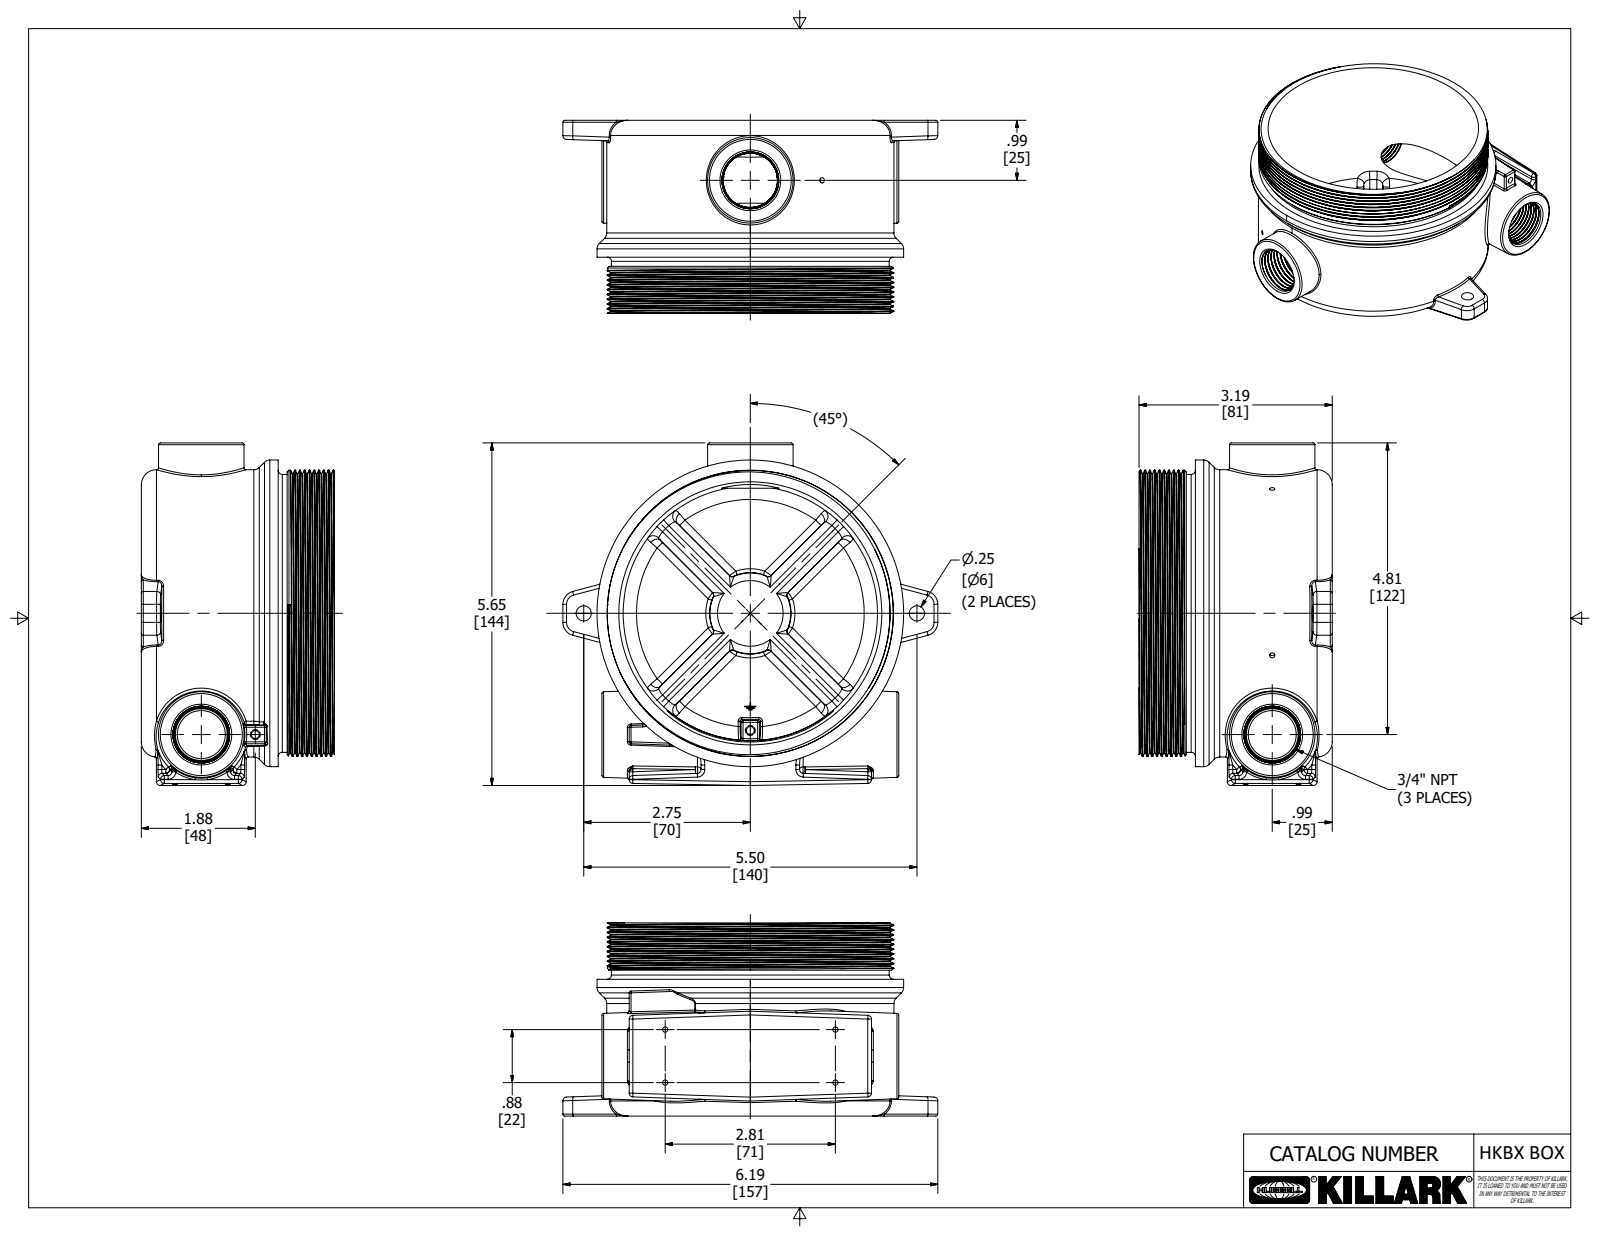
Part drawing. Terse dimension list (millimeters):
name: 51641ABAM for web
written by: Autodesk Inventor 2020 (AUTOMOTIVE_DESIGN)
unit: mm
bodies: 4 solids, 546 faces (207 planar, 96 cylindrical, 243 other)
size: 633.7 × 379.1 × 81
volume: 301 400 mm³; area: 302 100 mm²
holes: 2× ⌀3.3, 2× ⌀6.4, 1× ⌀20.1, 1× ⌀110.2
bosses: 1× ⌀128.5, 1× ⌀120.4, 1× ⌀120, 1× ⌀116.5, 1× ⌀35.8
rounds: 35× R1.6, 13× R0.8, 8× R3.2, 4× R5.6, 1× R1.6, 1× R19.1, 1× R52.7, 1× R54
face distances: 6.4, 12.7, 81, 74.6, 68.3, 57.4, 51, 44.7, 23.6, 12.1
hole spacings: 69.9, 85.4, 22.7, 49.1, 139.7
